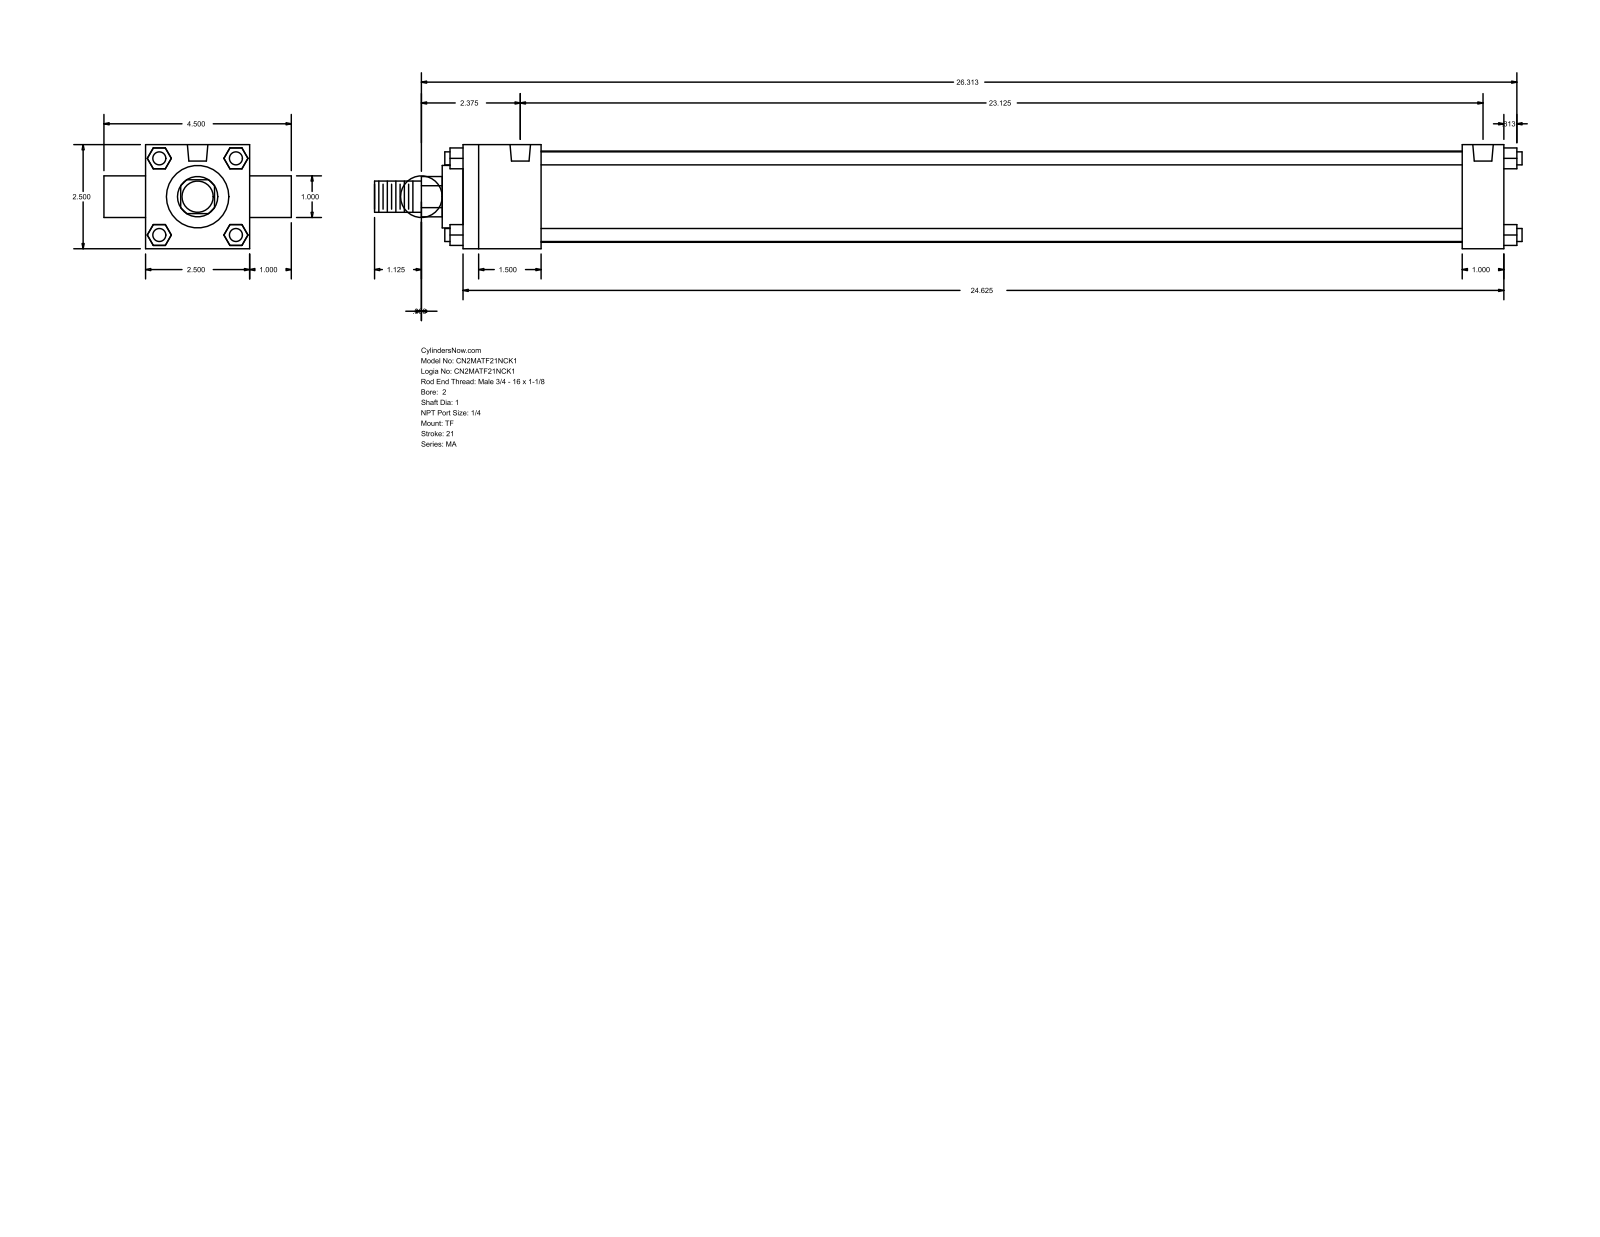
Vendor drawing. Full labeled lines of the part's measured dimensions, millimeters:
Part name (STEP PRODUCT): MA_TF__0200_1
STEP written by: GSSL Pune (CONFIG_CONTROL_DESIGN)
Units: millimetres
Bodies: 0 solids, 120 faces (92 planar, 28 cylindrical, 0 other)
Overall size (bounding box): 700.09 × 114.3 × 63.5
Round holes (diameter × count): ⌀7.94 ×3, ⌀12.49 ×2
Round bosses / shafts (diameter × count): ⌀7.94 ×4, ⌀25.4 ×2, ⌀55.63 ×1, ⌀38.1 ×1, ⌀19.05 ×1
Partial cylindrical surfaces — rounded edges, fillets, slot ends (radius × count): R12.29 ×1
Main face-to-face distances: 63.5, 25.4, 635, 12.7, 47.63, 609.6, 561.97, 587.37, 88.9, 23.37
Hole centre spacings: 587.37
